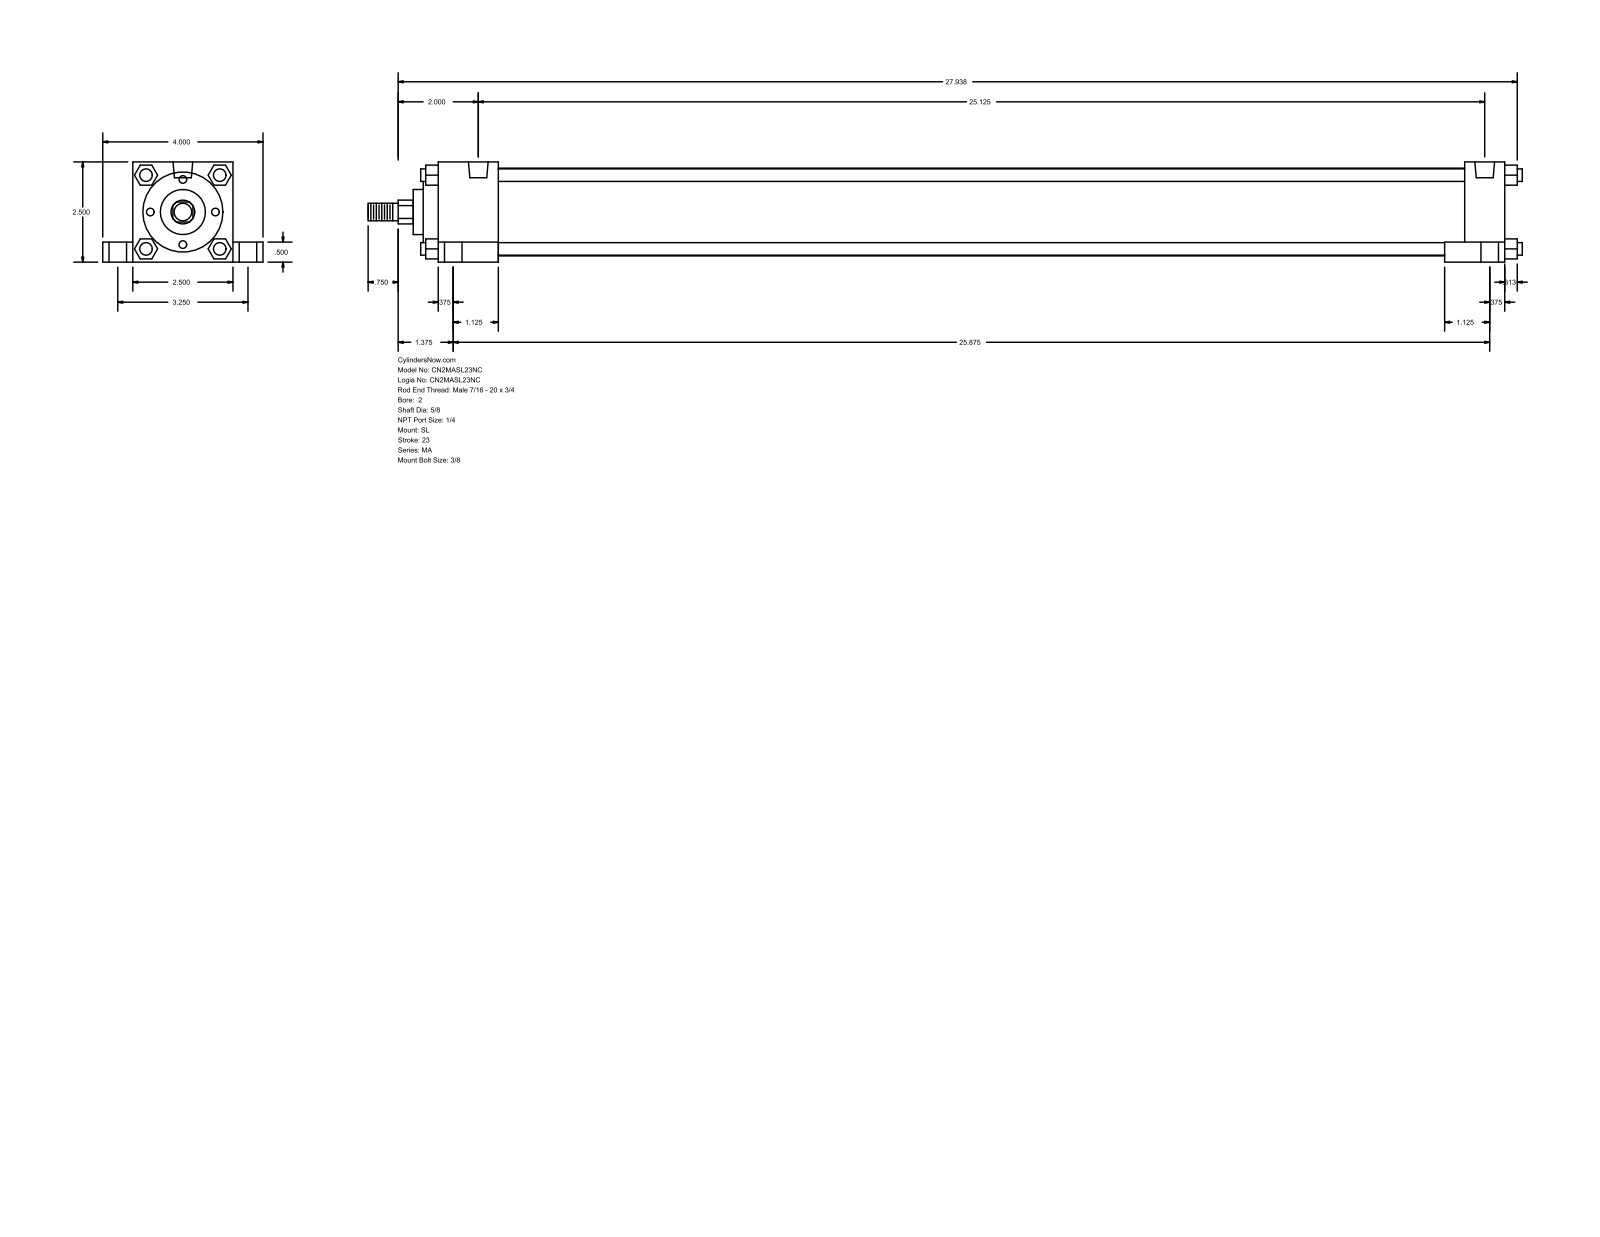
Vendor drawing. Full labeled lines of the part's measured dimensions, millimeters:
Part name (STEP PRODUCT): MA_SL__0200_0.625
STEP written by: GSSL Pune (CONFIG_CONTROL_DESIGN)
Units: millimetres
Bodies: 0 solids, 150 faces (113 planar, 37 cylindrical, 0 other)
Overall size (bounding box): 731.84 × 101.6 × 63.5
Round holes (diameter × count): ⌀7.94 ×4, ⌀11.11 ×4, ⌀17.46 ×4, ⌀12.49 ×2
Round bosses / shafts (diameter × count): ⌀7.94 ×4, ⌀55.63 ×1, ⌀50.8 ×1, ⌀28.57 ×1, ⌀15.88 ×1, ⌀11.11 ×1
Partial cylindrical surfaces — rounded edges, fillets, slot ends (radius × count): R7.54 ×1
Main face-to-face distances: 63.5, 12.7, 9.52, 612.77, 25.4, 19.05, 82.55, 38.1, 676.27, 50.8
Hole centre spacings: 41.39, 44.22, 82.54, 638.18, 642.68, 655.36, 657.23, 662.39
